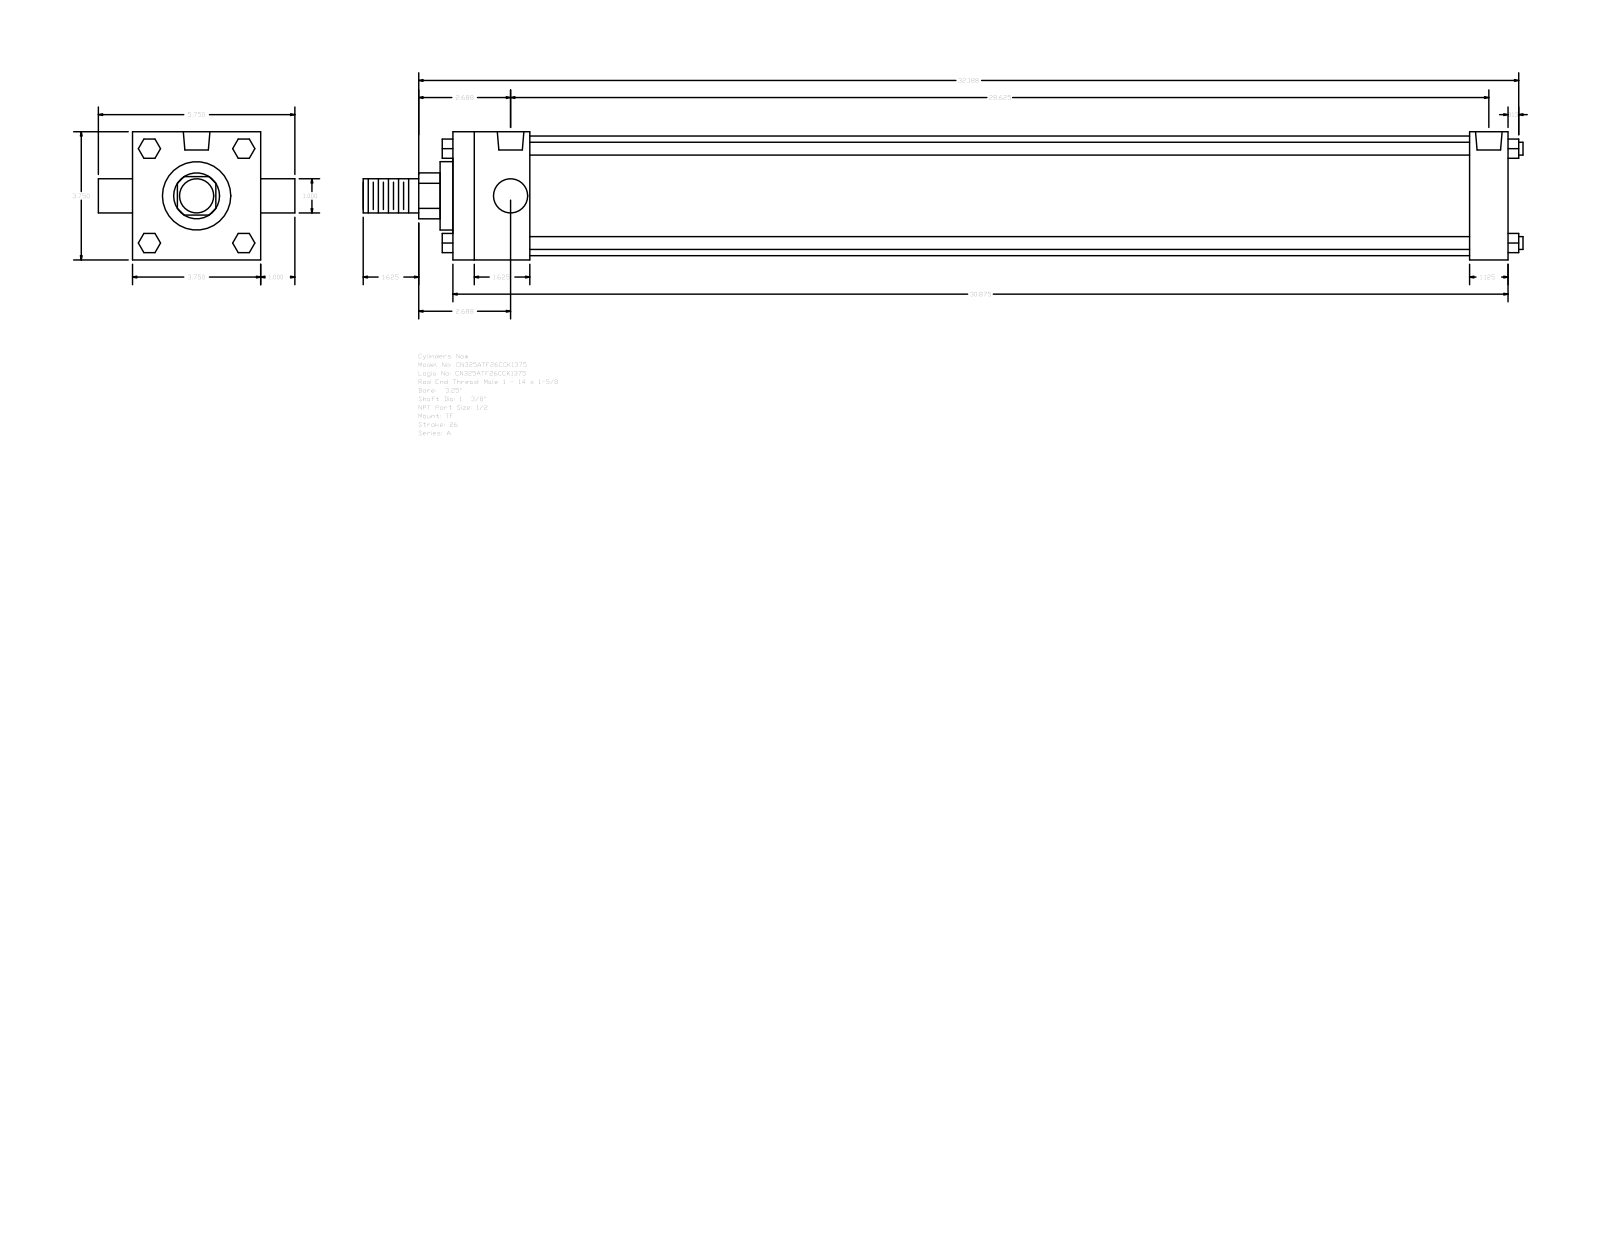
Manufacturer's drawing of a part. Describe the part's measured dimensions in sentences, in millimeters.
The part is named "A_TF__0325_1.375". Its 3-D file was written by "GSSL Pune (CONFIG_CONTROL_DESIGN)". It is 0 solids with 120 faces: 92 planar, 28 cylindrical and 0 other. Overall it measures 862.01 by 146.05 by 95.25 millimeters. Round holes: 3 of diameter 8.73, 2 of diameter 19.77. Round bosses or shafts: 4 of diameter 9.53, 2 of diameter 25.4, 1 of diameter 88.9, 1 of diameter 50.8, 1 of diameter 34.92. Partial cylindrical surfaces (rounded edges, fillets, slot ends): 1 of radius 17.06. The main face-to-face distances are 95.24, 784.22, 57.15, 755.65, 698.5, 727.07, 28.57, 66.67, 9.52, 765.17. The hole center spacings are 3.18, 723.9, 720.72, 727.08.
